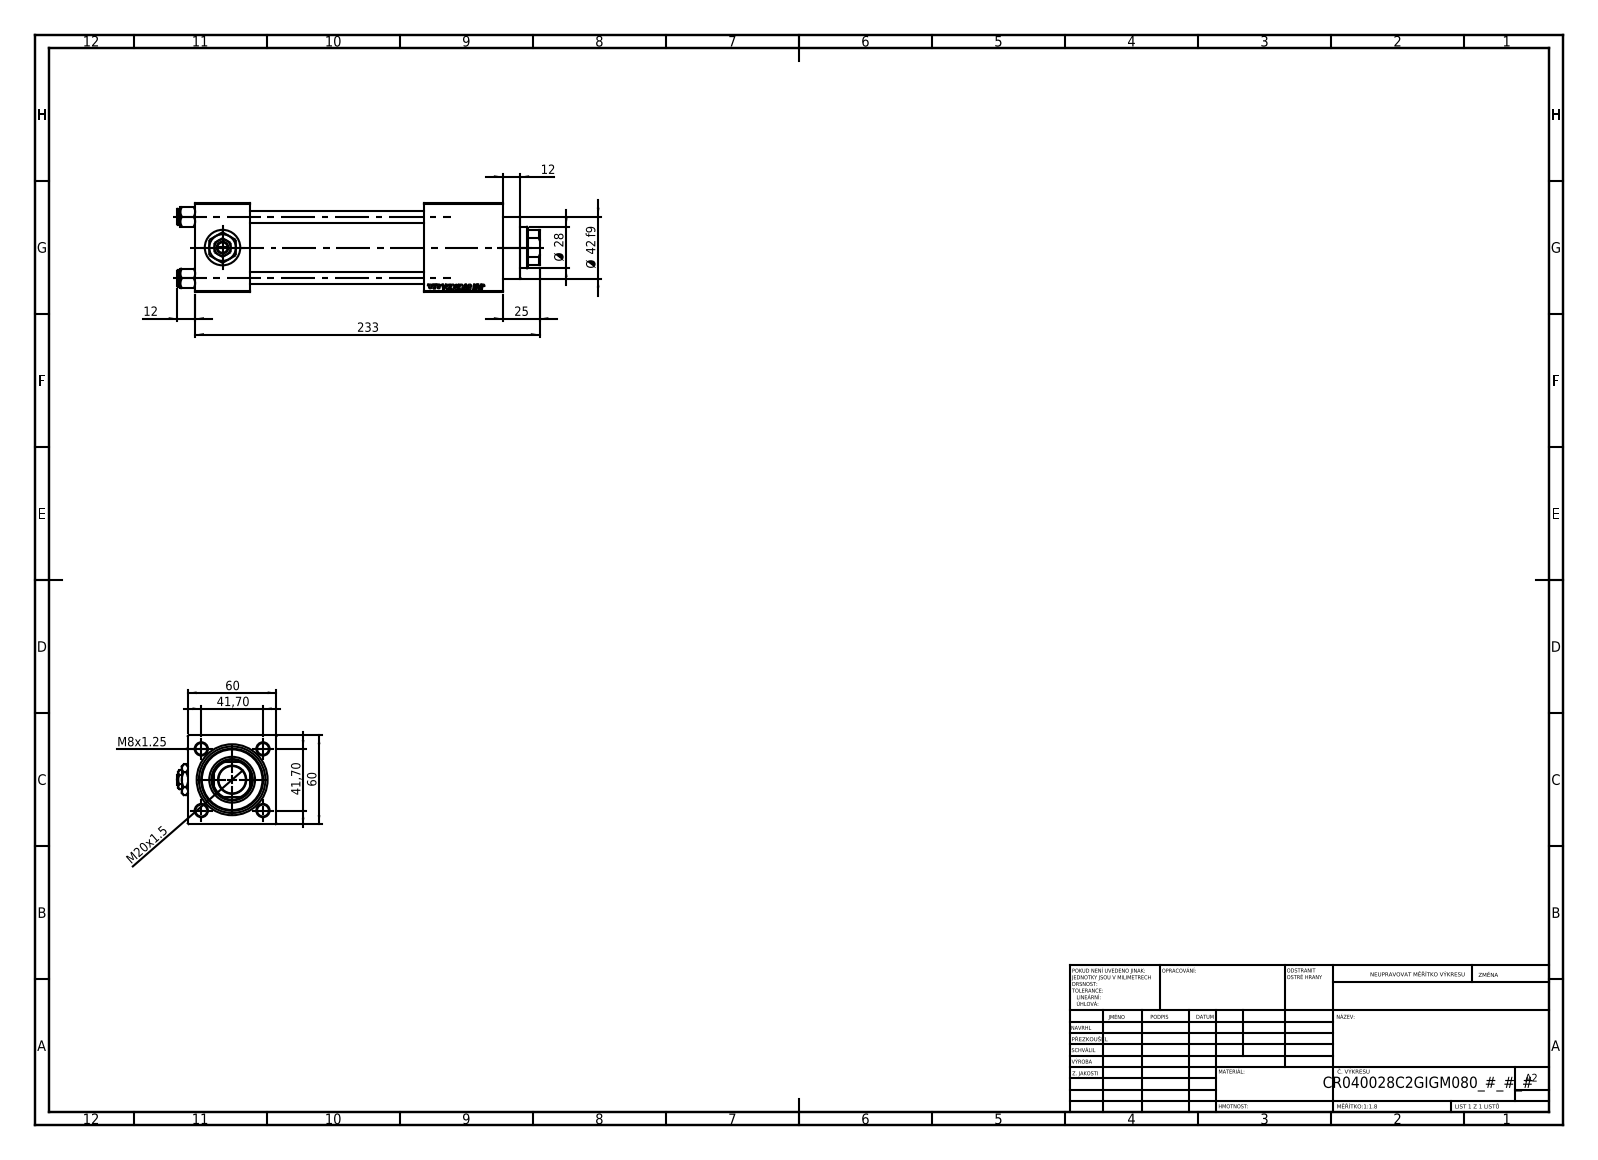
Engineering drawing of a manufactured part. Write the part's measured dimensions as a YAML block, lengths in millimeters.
part_name: "Zatka_pro_OIL_PORT; V215CR_C_TYCINKA; V215_VC_A; NUT_M5_C (+2 more)"
step_written_by: "SolidWorks 2019 (CONFIG_CONTROL_DESIGN)"
units: millimeters
bodies: {solids: 12, faces: 1202, planar: 550, cylindrical: 94, other: 558}
overall_size: [245, 67, 60]
volume: 496152
surface_area: 140604
round_holes:
  - {diameter: 8, count: 4}
  - {diameter: 7, count: 2}
  - {diameter: 16.66, count: 2}
  - {diameter: 24, count: 2}
  - {diameter: 18.5, count: 1}
  - {diameter: 28, count: 1}
  - {diameter: 31, count: 1}
  - {diameter: 40, count: 1}
  - {diameter: 45, count: 1}
round_bosses_or_shafts:
  - {diameter: 11, count: 4}
  - {diameter: 46, count: 1}
  - {diameter: 42, count: 1}
partial_cylinders:
  - {radius: 13.5, count: 1}
face_to_face_distances: [60, 37, 155, 118, 179.3, 142.3, 24.3, 53, 208, 171]
hole_center_spacings: [29.49, 41.7, 58.97]
